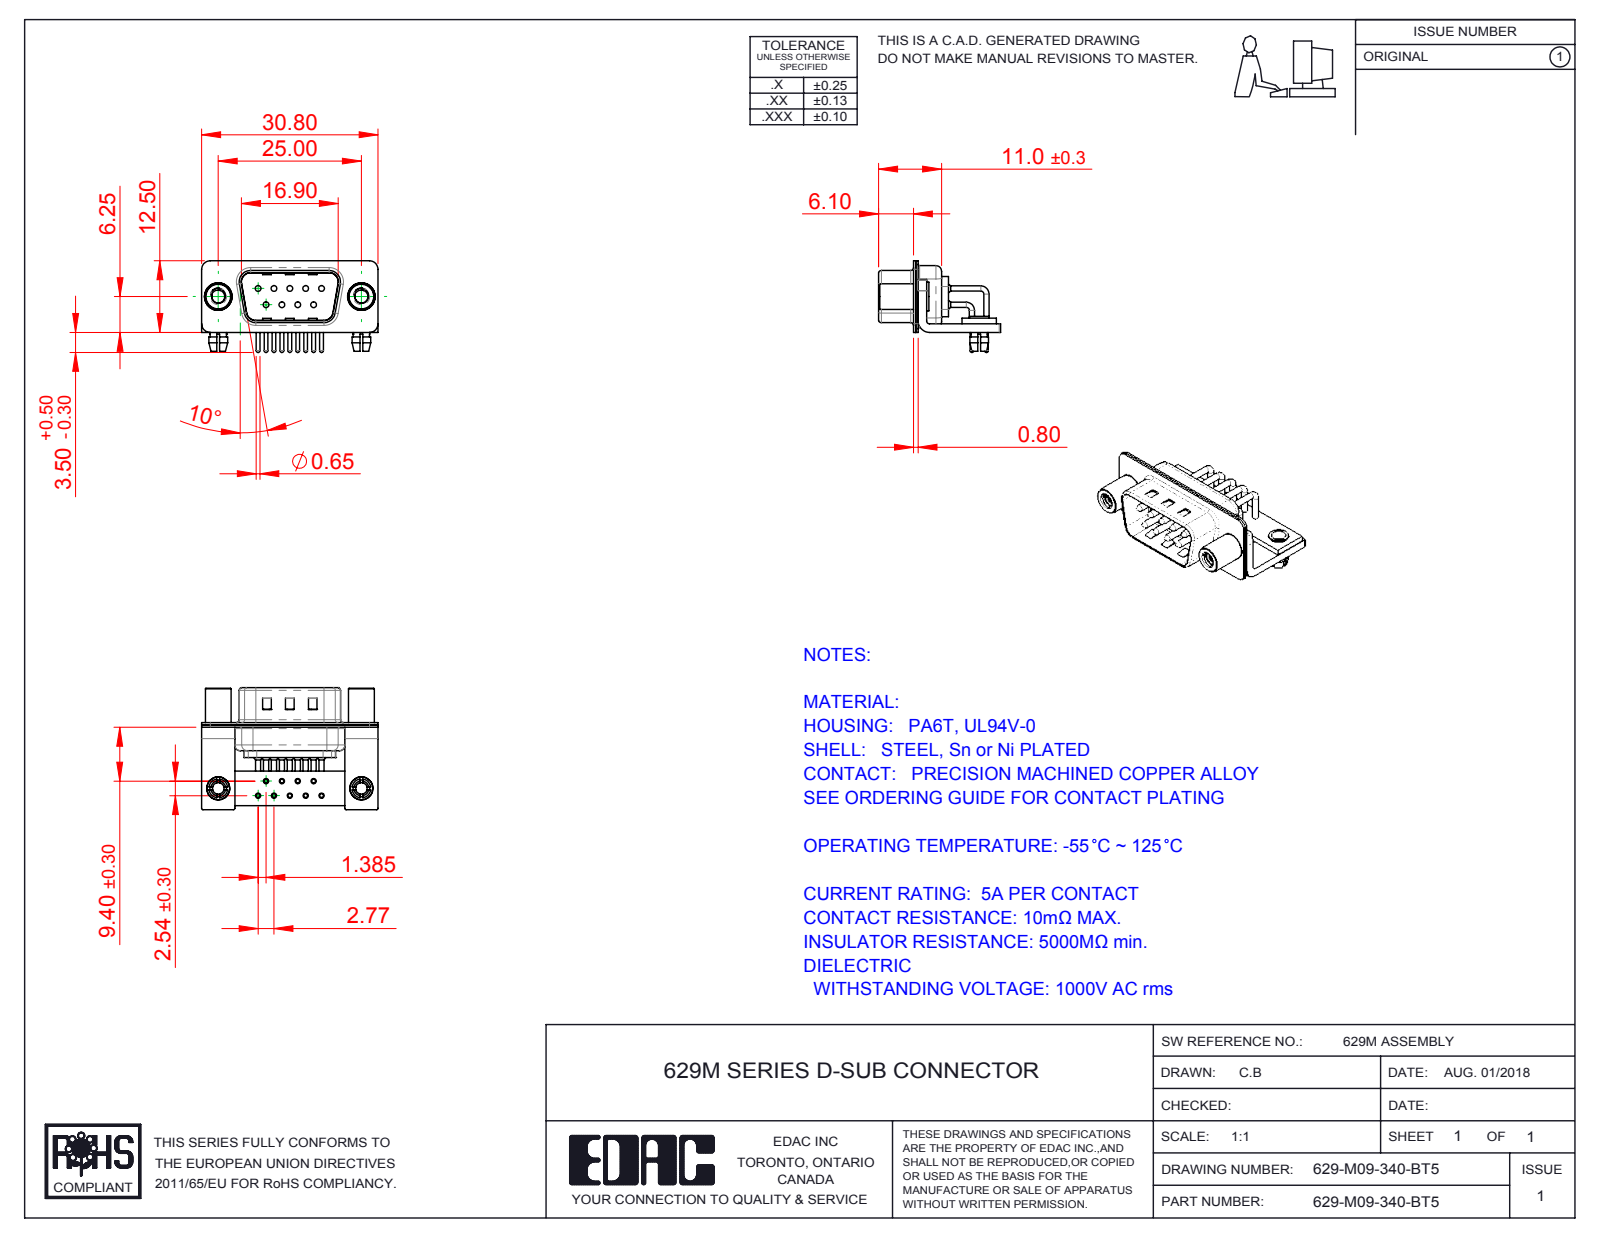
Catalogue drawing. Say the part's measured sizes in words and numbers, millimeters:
The part is named "629M 4-40 Threaded Standoff; 629M Board Lock; 629M Shell Front_09 Contacts; 629M Stabilizer Board_09 Contacts (+6 more)". Its 3-D file was written by "SolidWorks 2016 (CONFIG_CONTROL_DESIGN)". It is 19 solids with 1504 faces: 759 planar, 567 cylindrical and 178 other. Overall it measures 30.8 by 21.3 by 16 millimeters. Its volume is 1 984 cubic millimeters and its surface area 5 510 square millimeters. Round holes: 11 of diameter 2, 9 of diameter 0.9, 9 of diameter 1, 9 of diameter 1.7, 2 of diameter 2.26, 2 of diameter 2.5, 2 of diameter 3.2, 2 of diameter 4, 2 of diameter 4.8. Round bosses or shafts: 9 of diameter 1.5, 9 of diameter 0.9, 9 of diameter 0.65, 2 of diameter 5, 2 of diameter 4.9, 2 of diameter 4.5, 2 of diameter 4, 2 of diameter 3.4. Partial cylindrical surfaces (rounded edges, fillets, slot ends): 16 of radius 0.25, 16 of radius 1.5, 13 of radius 2, 9 of radius 0.5, 9 of radius 1.01, 8 of radius 1.6, 4 of radius 0.6, 4 of radius 0.65. The main face-to-face distances are 0.4, 1.5, 0.8, 0.85, 1.25, 1.9, 1, 2.5, 10.4, 9.55. The hole center spacings are 2.77, 5.54, 3.16, 4.87, 8.31, 2.89, 2.9, 5.03.
